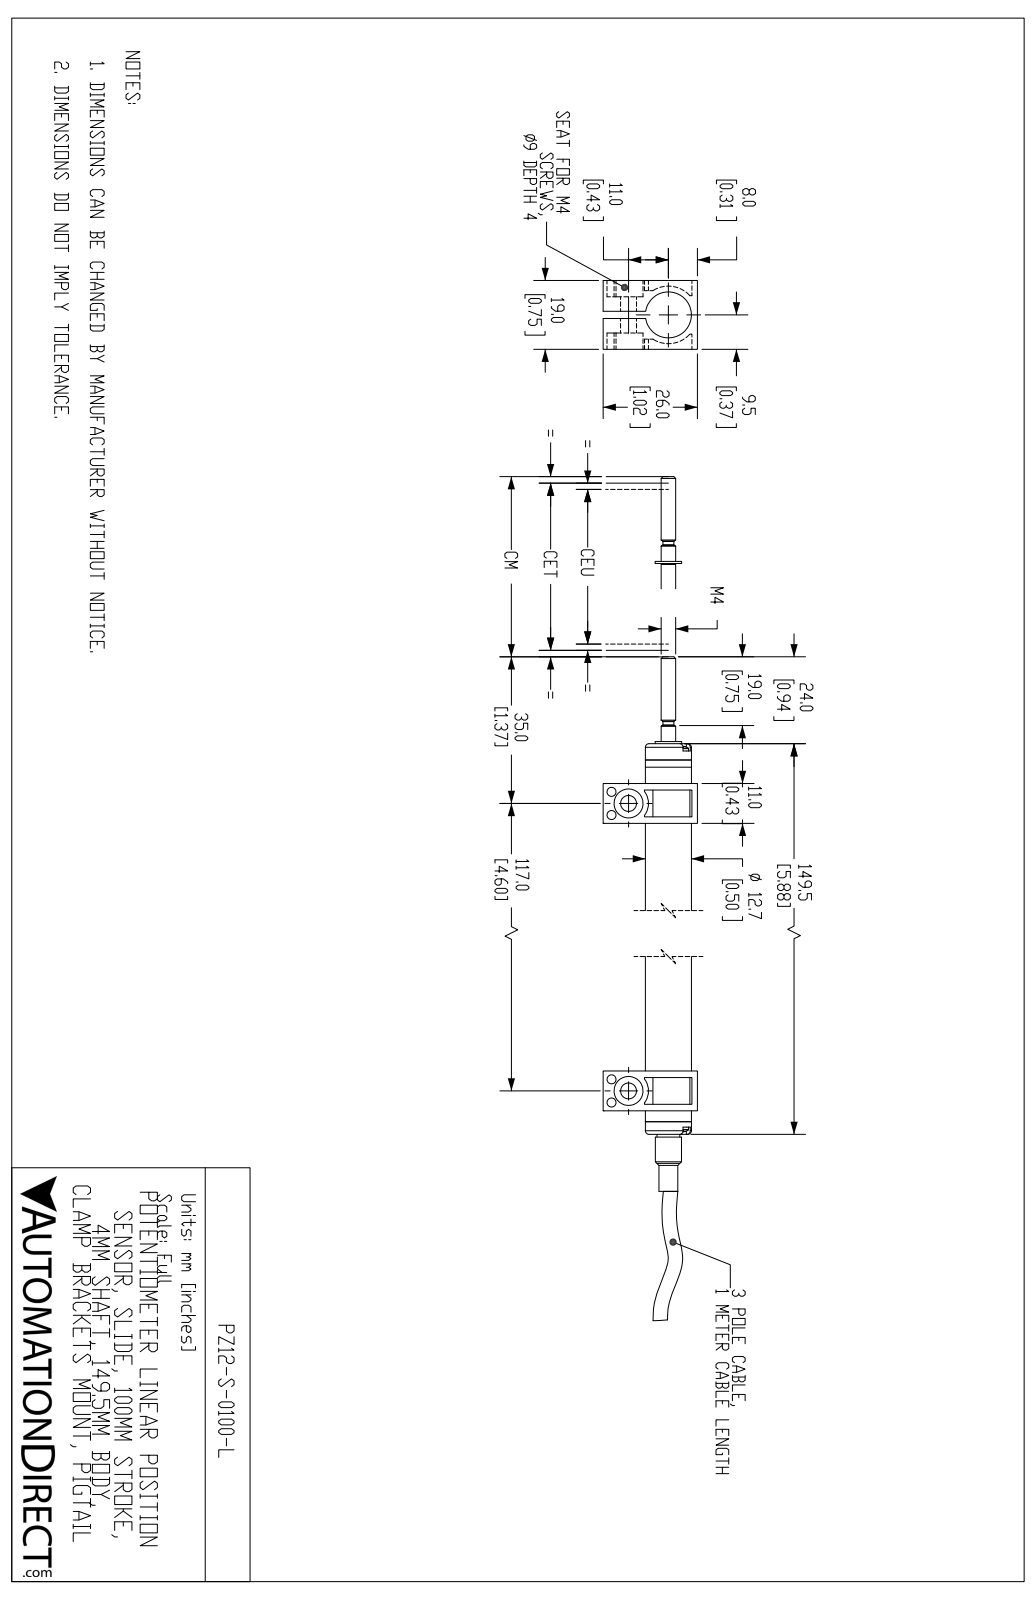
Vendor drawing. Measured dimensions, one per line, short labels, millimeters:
name: PZ12-S-0100-L
written by: SolidWorks 2019 (AUTOMOTIVE_DESIGN)
unit: mm
bodies: 14 solids, 594 faces (198 planar, 164 cylindrical, 232 other)
size: 224.9 × 26 × 19
volume: 26 430 mm³; area: 17 860 mm²
holes: 4× ⌀2.5, 2× ⌀1.4, 2× ⌀1.5, 2× ⌀2, 2× ⌀4.4, 2× ⌀8, 1× ⌀1, 1× ⌀3.2, 1× ⌀3.5, 1× ⌀5.1, 1× ⌀5.6, 1× ⌀6
bosses: 2× ⌀3.2, 2× ⌀1.6, 2× ⌀0.5, 1× ⌀12.7, 1× ⌀7.2, 1× ⌀6.3, 1× ⌀5.2, 1× ⌀4
rounds: 4× R0.3, 2× R0.5, 2× R0.7, 2× R1.8, 2× R5.5, 1× R0.4, 1× R2.6, 1× R3.7
face distances: 117, 11, 1, 2, 8.5, 10.5, 26, 106, 128, 10
hole spacings: 5.7, 117, 4.8, 5, 5.4, 6.4, 8.2, 113.9
